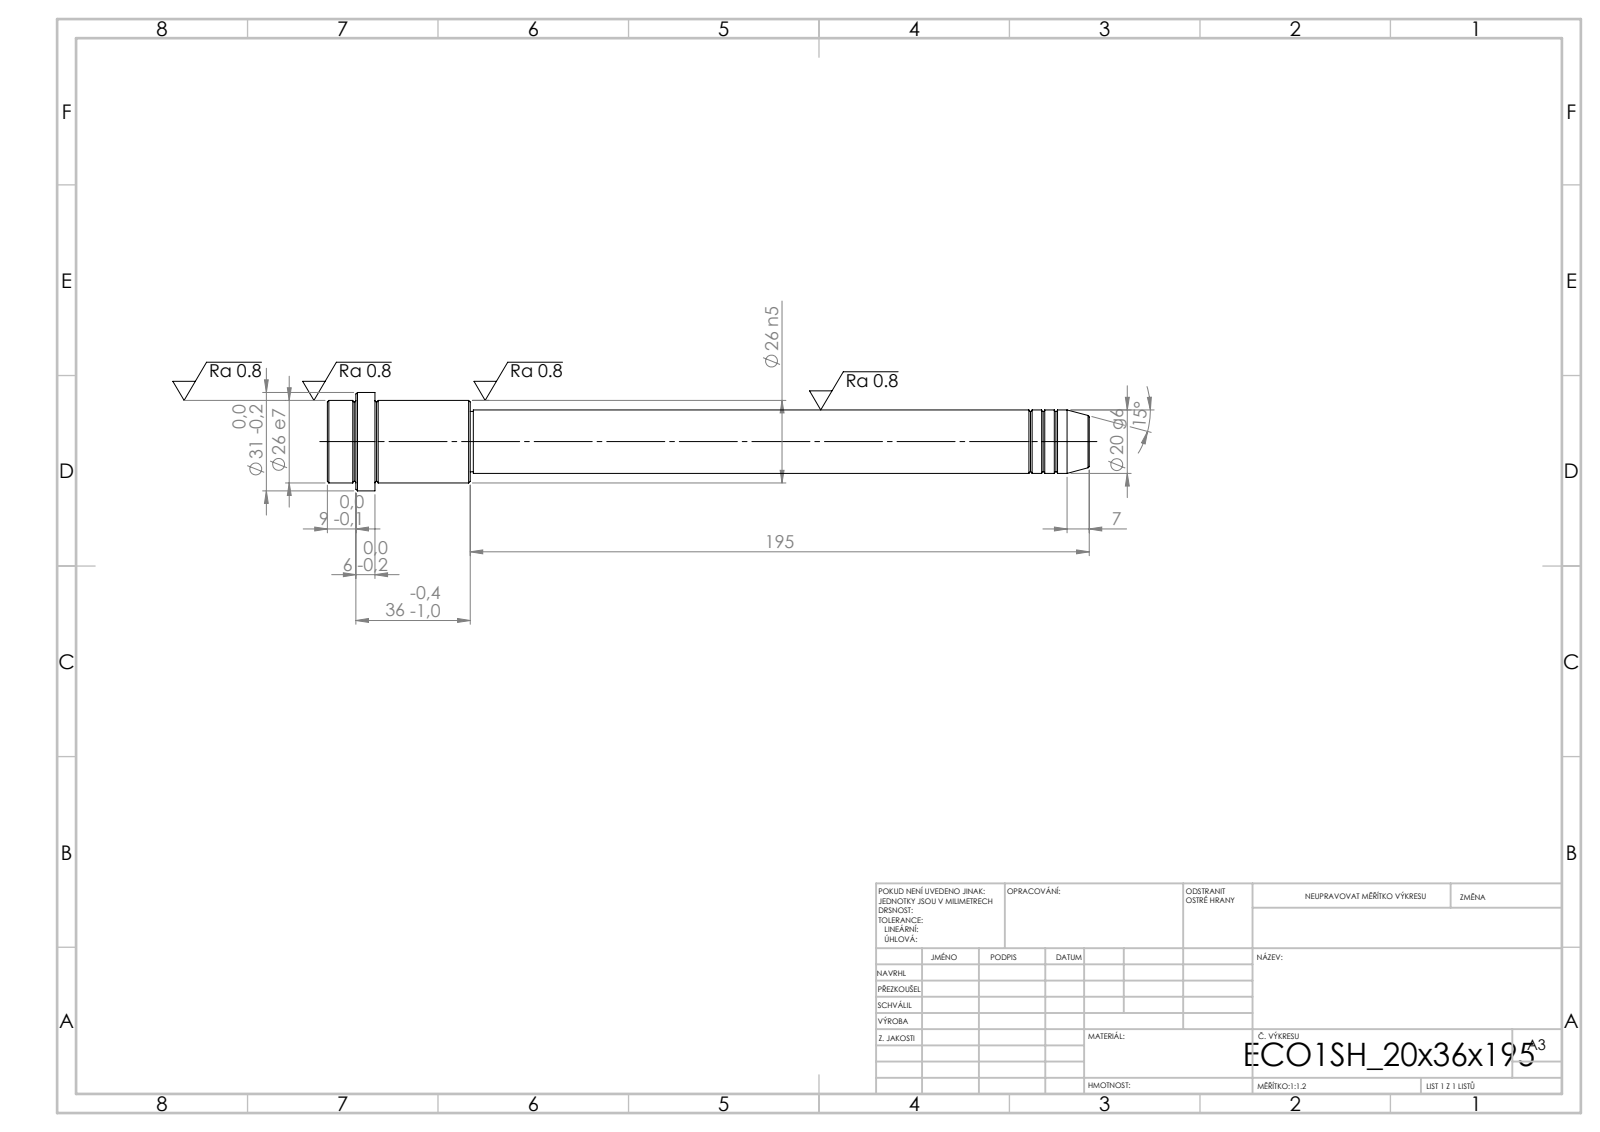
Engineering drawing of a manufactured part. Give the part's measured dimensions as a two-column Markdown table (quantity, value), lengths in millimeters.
| quantity | value |
| --- | --- |
| STEP written by | SolidWorks 2019 (CONFIG_CONTROL_DESIGN) |
| units | millimeters |
| bodies | 1 solid, 52 faces (6 planar, 16 cylindrical, 30 other) |
| overall size | 240 × 31 × 31 |
| volume | 85 909 mm³ |
| surface area | 17 558 mm² |
| round bosses / shafts (diameter × count) | 31 × 1, 26 × 1, 20 × 1, 19 × 1 |
| main face-to-face distances | 15, 30, 45, 195, 225, 240, 231, 36, 6, 9 |
